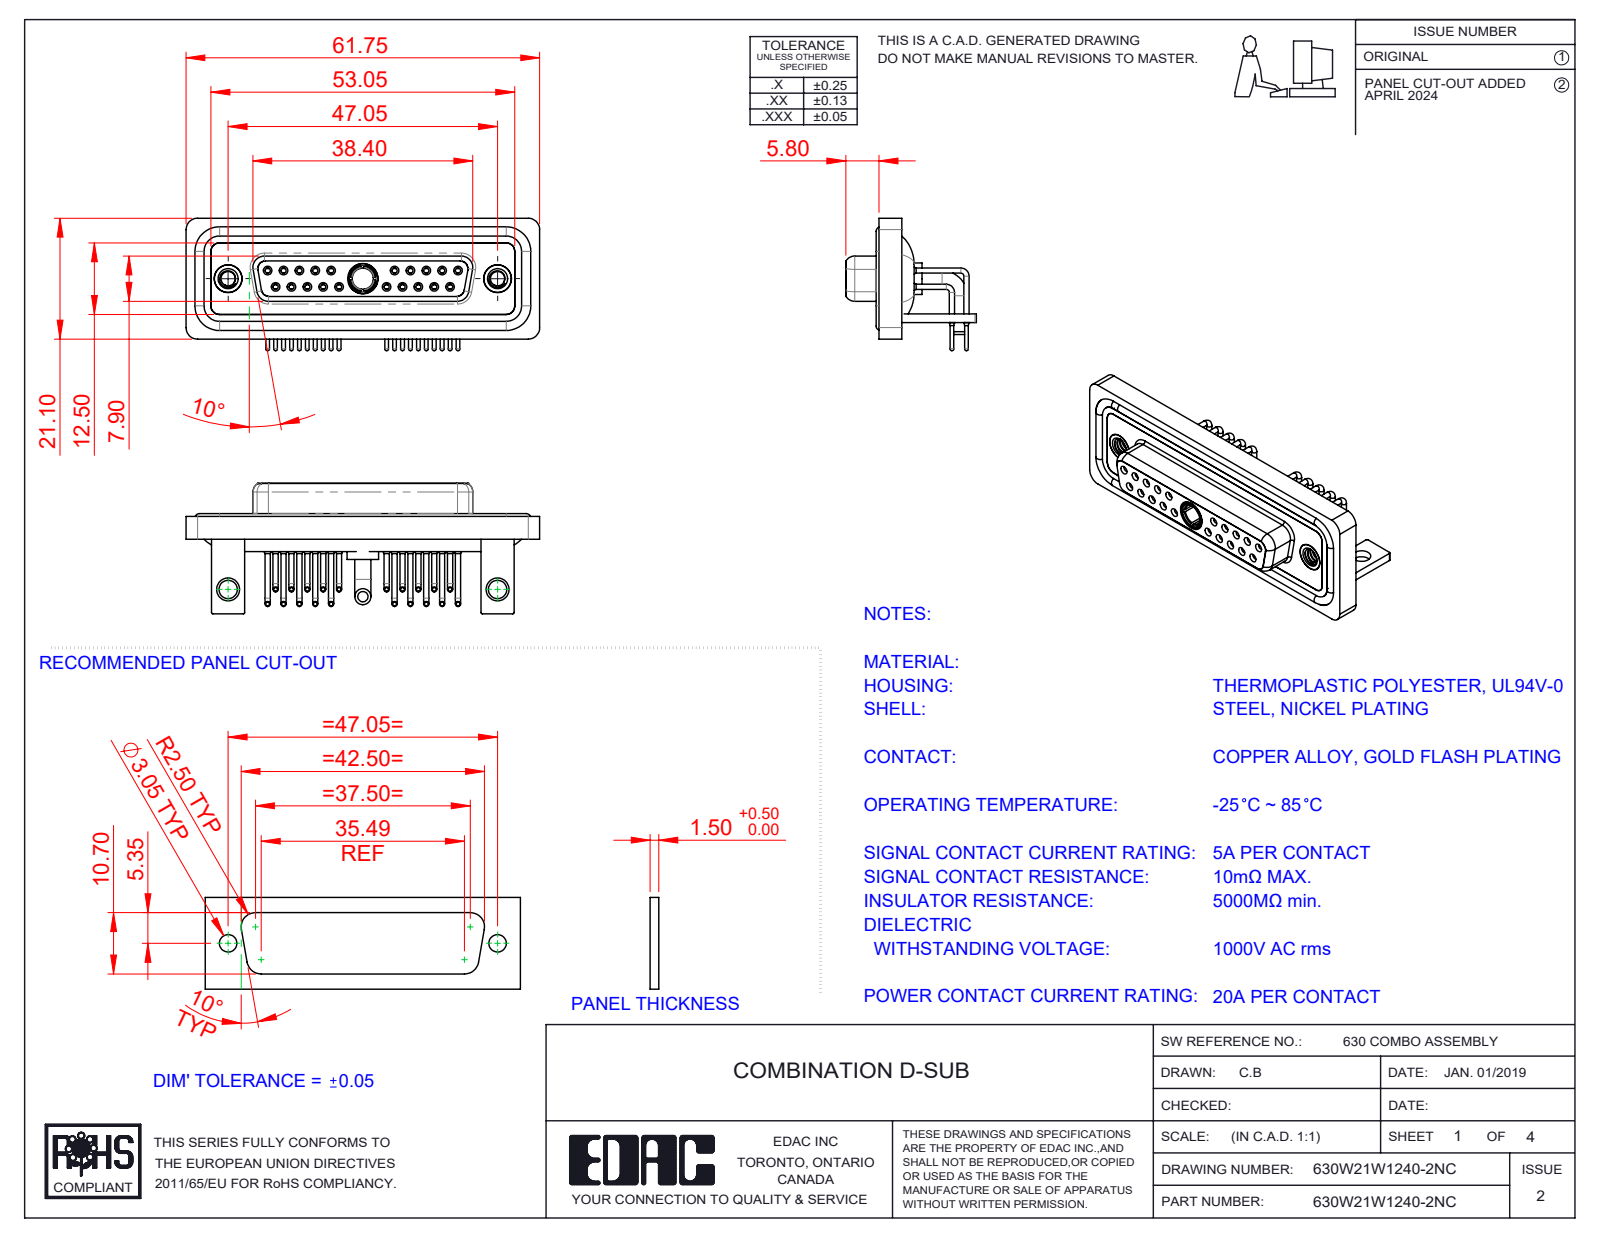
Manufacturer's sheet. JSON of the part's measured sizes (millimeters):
{"part_name": "630Combo Waterproof Housing_25 Contacts; 630Combo Housing_21W1; 630Combo Threaded Rivet_A; 630Combo Contact Row 1_50 Contacts (+6 more)", "step_written_by": "SolidWorks 2023 (CONFIG_CONTROL_DESIGN)", "units": "millimeters", "bodies": {"solids": 31, "faces": 1566, "planar": 454, "cylindrical": 695, "other": 417}, "overall_size": [61.75, 23.12, 22.8], "volume_mm3": 8865, "surface_area_mm2": 15518, "round_holes": [[0.9, 20], [1.1, 20], [1.5, 20], [2, 20], [1.6, 10], [1.7, 10], [4.85, 3], [2.5, 2], [3.2, 2], [4, 2], [4.05, 2], [5, 2]], "round_bosses_or_shafts": [[0.9, 20], [0.65, 20], [1.6, 14], [4.95, 2], [4.8, 2], [2.8, 2], [5.5, 1], [5.2, 1]], "partial_cylinders_radius": [[2, 19], [1.5, 18], [0.25, 16], [1.35, 8], [1.6, 8], [0.5, 5], [0.6, 4], [0.65, 4]], "face_to_face_distances": [0.4, 1.8, 2.9, 3.7, 1.5, 4.1, 1.1, 1.4, 1.6, 2.5], "hole_center_spacings": [3.16, 2.77, 5.54, 8.31, 5.04, 19.39, 20.97, 22.16]}
